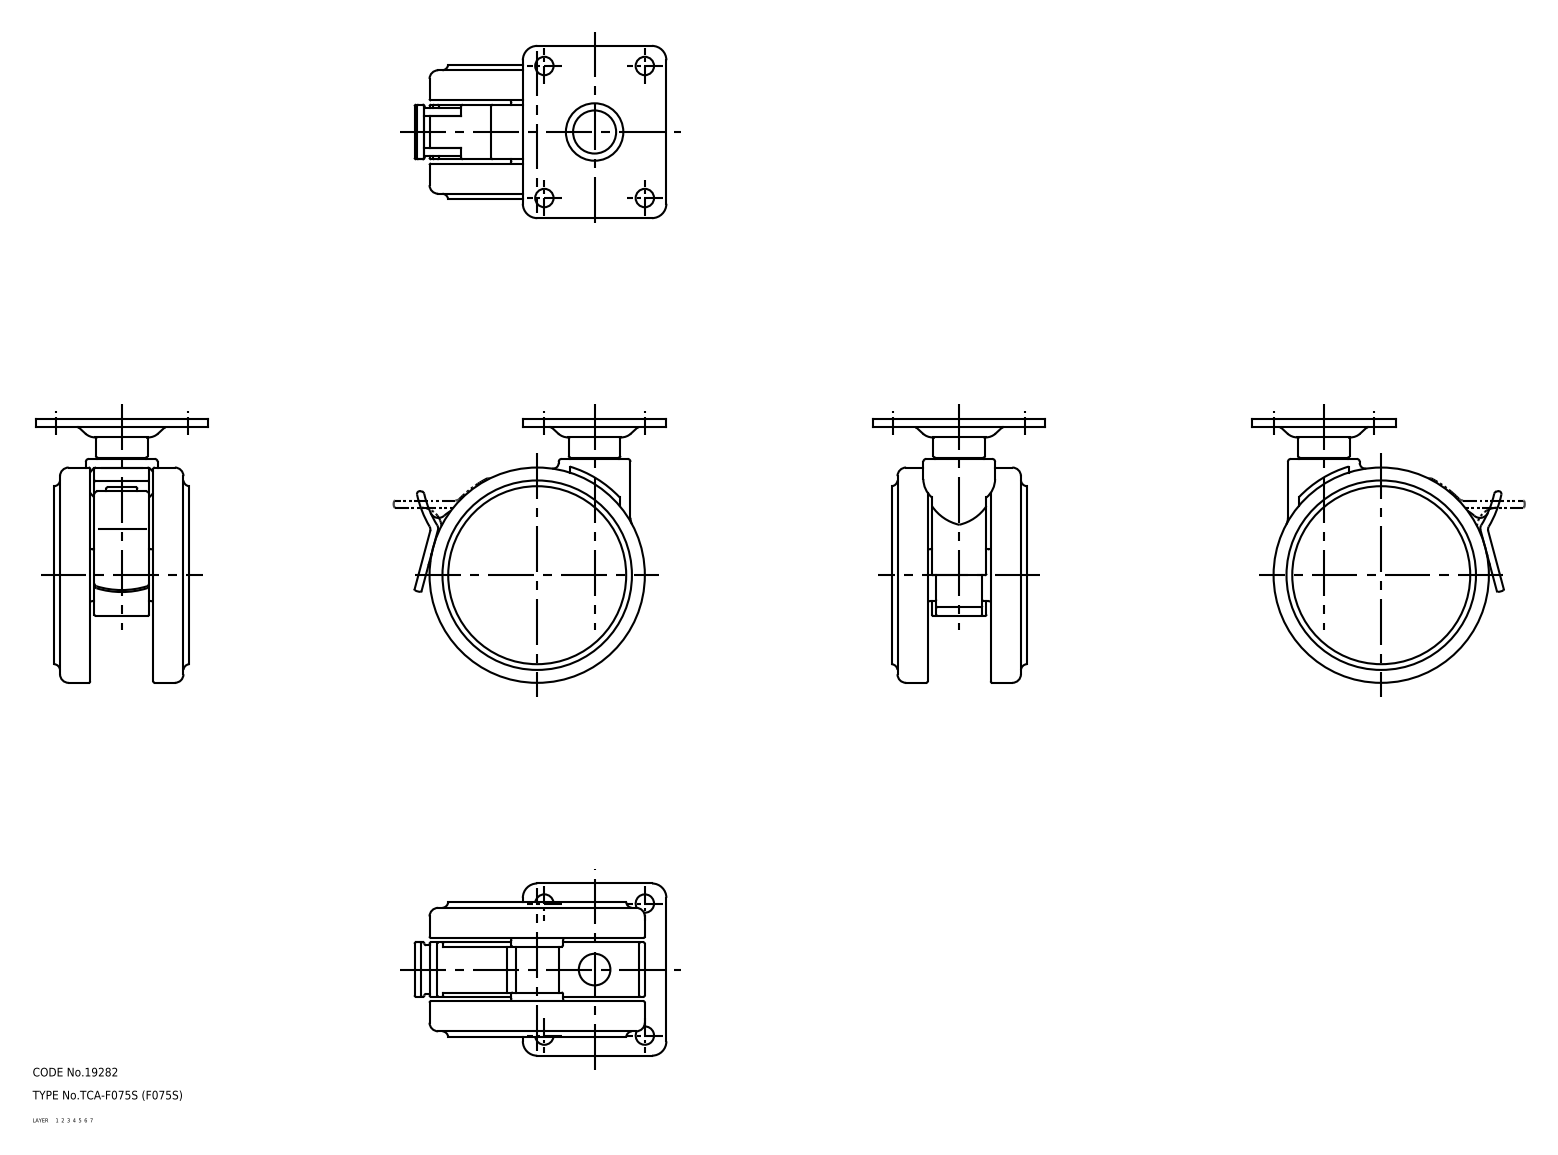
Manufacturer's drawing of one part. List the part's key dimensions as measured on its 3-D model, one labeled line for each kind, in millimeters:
Part name (STEP PRODUCT): 67126494; 67126507; 67126520; 67126533 (+2 more)
STEP written by: CADfix (AUTOMOTIVE_DESIGN)
Units: millimetres
Bodies: 6 solids, 278 faces (0 planar, 0 cylindrical, 278 other)
Overall size (bounding box): 92 × 87.75 × 60
Volume: 164 093 mm³ · Surface area: 46 030 mm²
